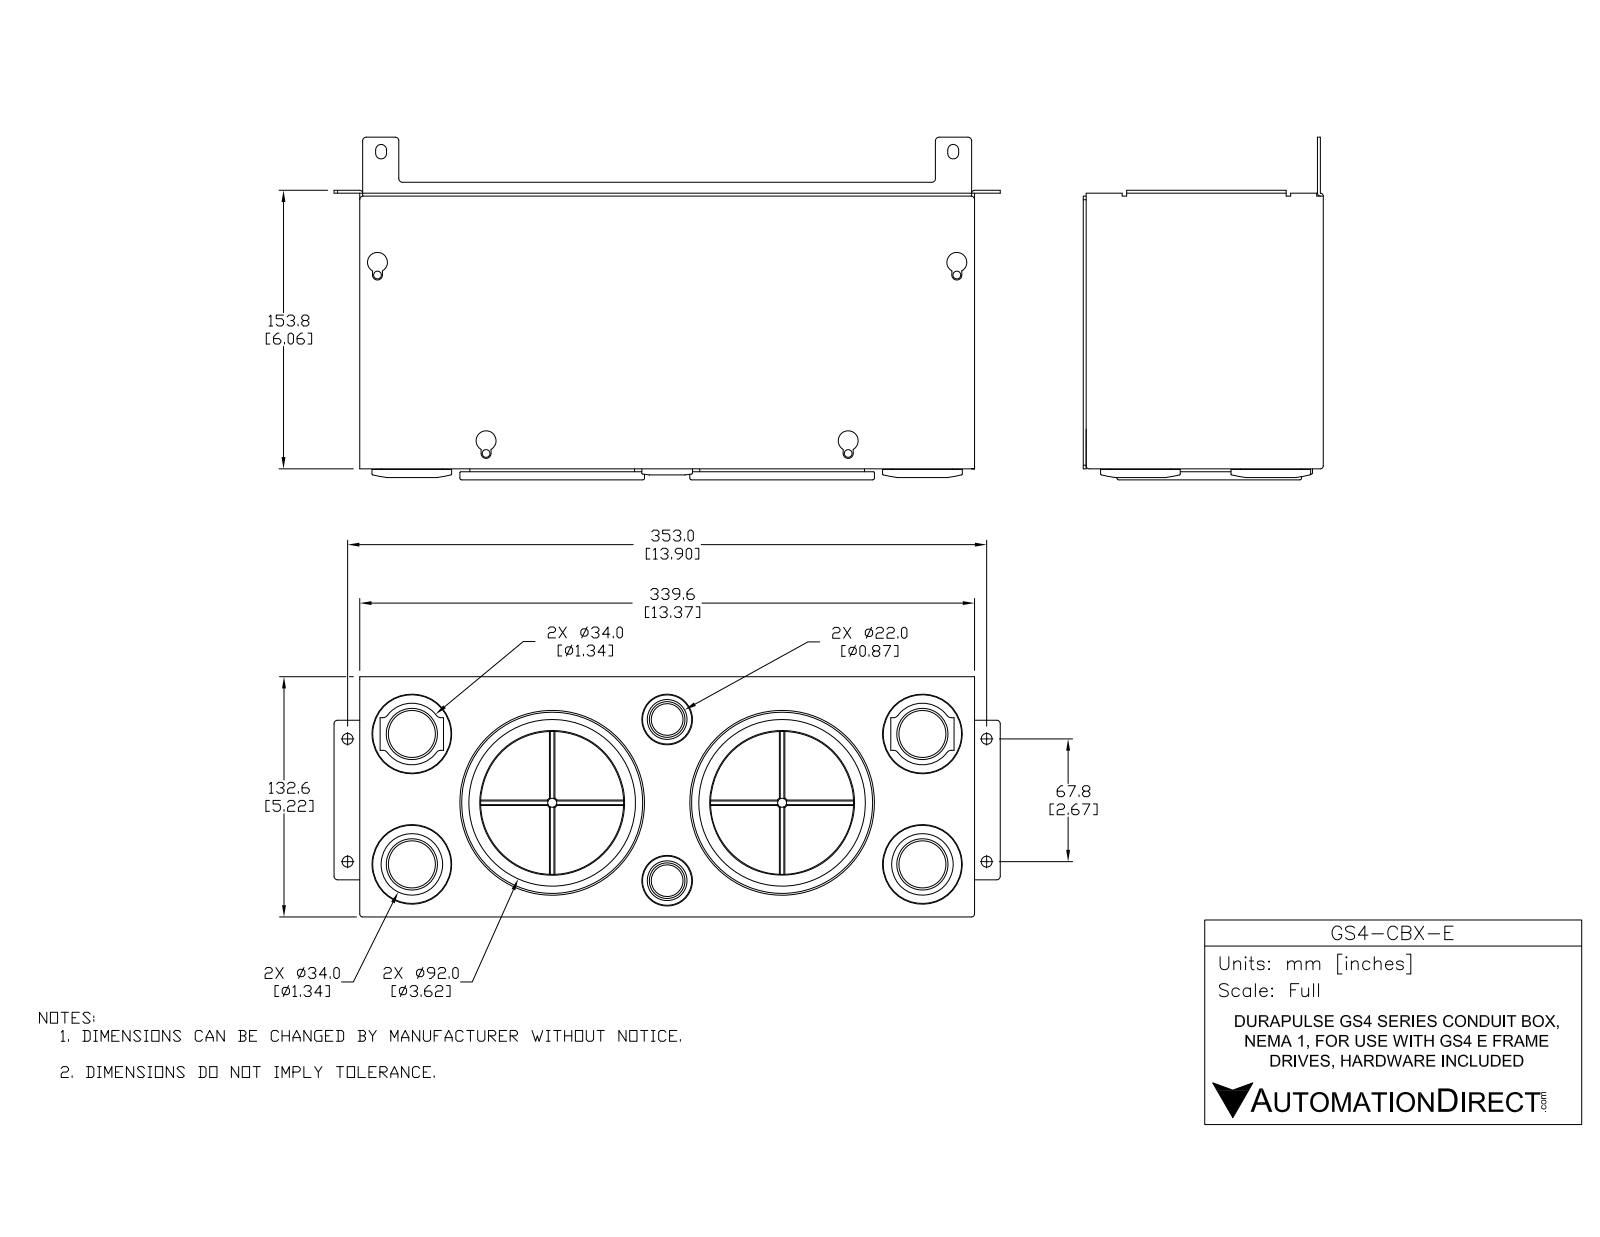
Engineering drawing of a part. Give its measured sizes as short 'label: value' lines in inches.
name: GS4-CBX-E
written by: SolidWorks 2015 (AUTOMOTIVE_DESIGN)
unit: in
bodies: 0 solids, 277 faces (132 planar, 69 cylindrical, 76 other)
size: 14.488 × 7.449 × 5.433
bosses: 4× ⌀1.043, 4× ⌀0.295, 4× ⌀0.169, 2× ⌀3.268, 2× ⌀3.11, 2× ⌀0.65
rounds: 9× R0.063, 9× R0.079, 2× R0.126, 2× R0.866, 1× R0.02, 1× R0.551
face distances: 0.063, 5.157, 5.094, 5.22, 13.307, 0.126, 13.37, 13.244, 5.031, 0.185
